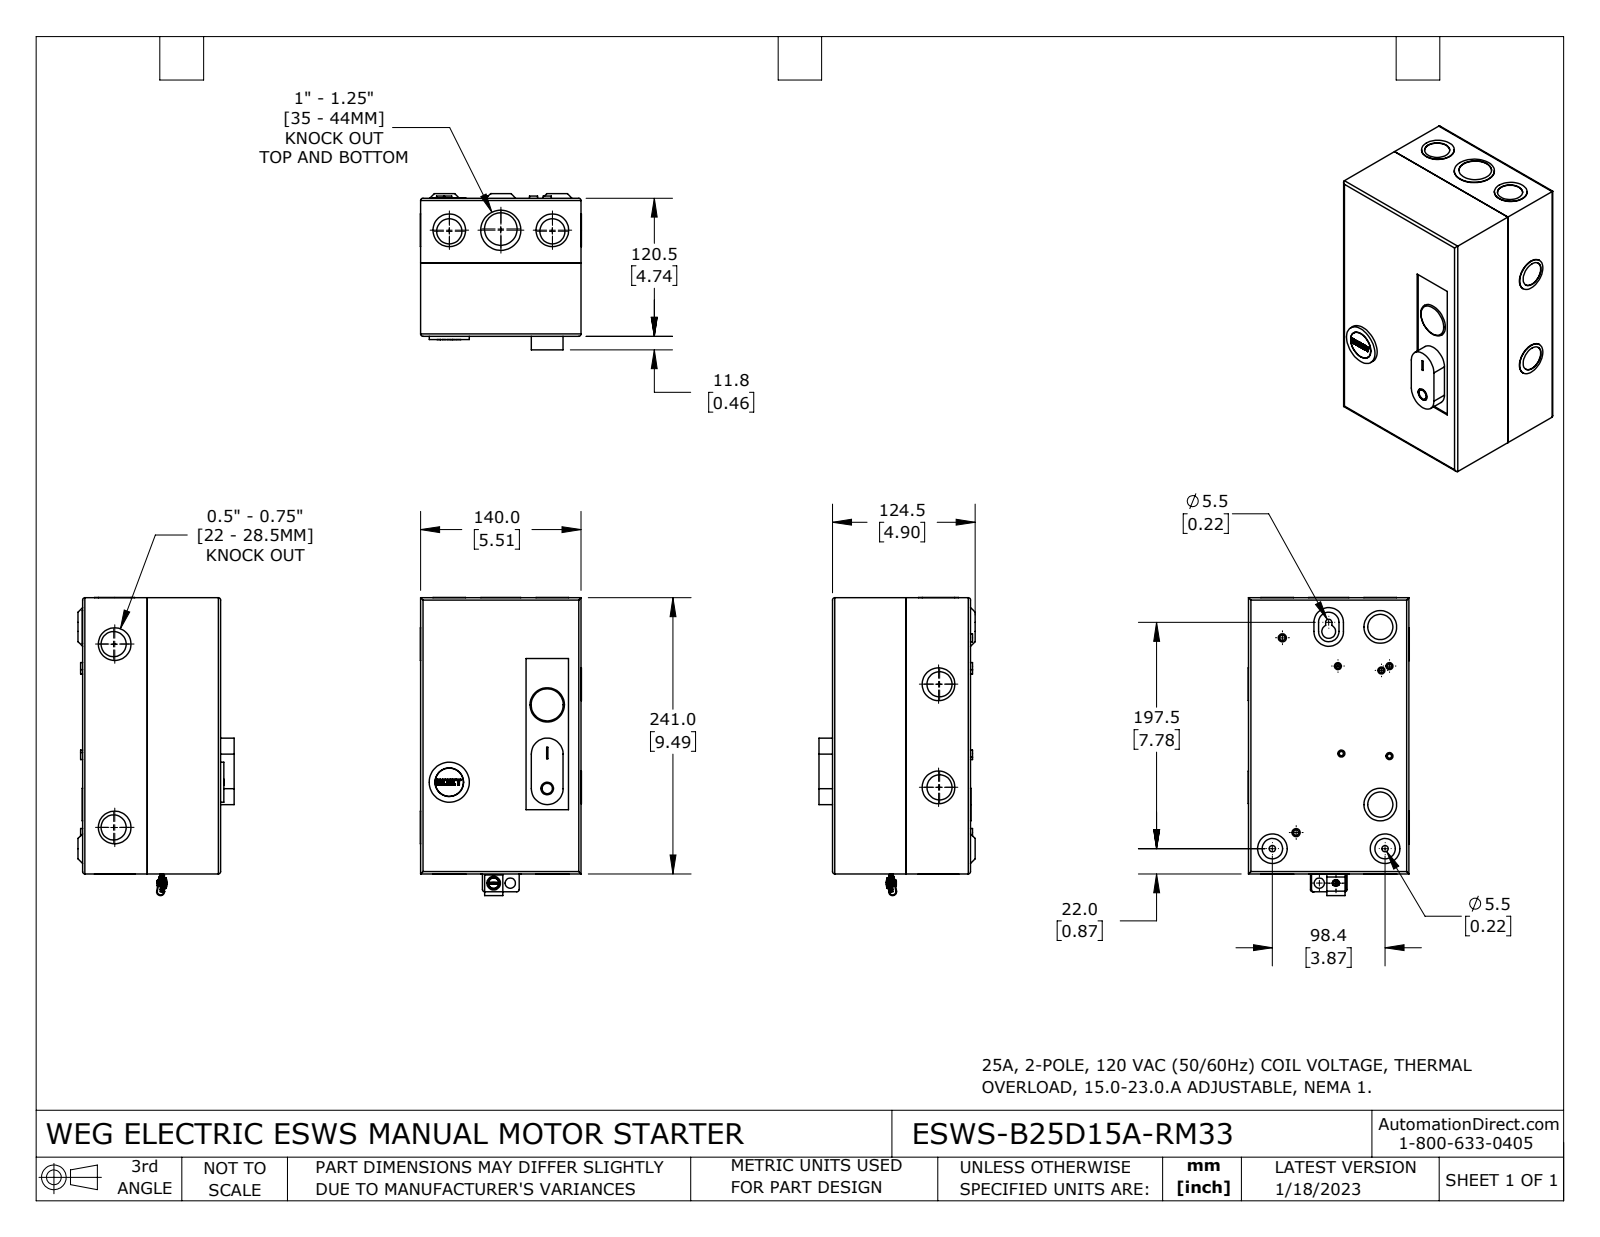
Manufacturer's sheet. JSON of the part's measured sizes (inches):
{"part_name": "ESWS-B25D15A-RM33", "step_written_by": "SolidWorks 2021 (CONFIG_CONTROL_DESIGN)", "units": "inches", "bodies": {"solids": 7, "faces": 435, "planar": 168, "cylindrical": 230, "other": 37}, "overall_size": [10.248, 5.535, 5.366], "volume_in3": 16.23, "surface_area_in2": 585.2, "round_holes": [[0.146, 5], [0.864, 4], [0.183, 2], [0.217, 2], [0.354, 2], [0.864, 2], [0.866, 2], [0.886, 2], [0.256, 1], [0.303, 1], [0.433, 1], [0.469, 1]], "round_bosses_or_shafts": [[1.124, 6], [0.24, 5], [1.122, 2], [0.278, 2], [1.38, 1], [1.378, 1], [1.193, 1], [1.148, 1]], "partial_cylinders_radius": [[0.004, 34], [0.079, 13], [0.031, 4], [0.108, 3], [0.059, 2], [0.075, 2], [0.122, 2], [0.138, 2]], "face_to_face_distances": [0.047, 4.697, 5.465, 4.65, 9.441, 4.744, 5.417, 5.512, 0.071, 0.063], "hole_center_spacings": [0.571, 1.378, 1.773, 3.387, 3.543, 4.921, 5.995, 7.484]}
